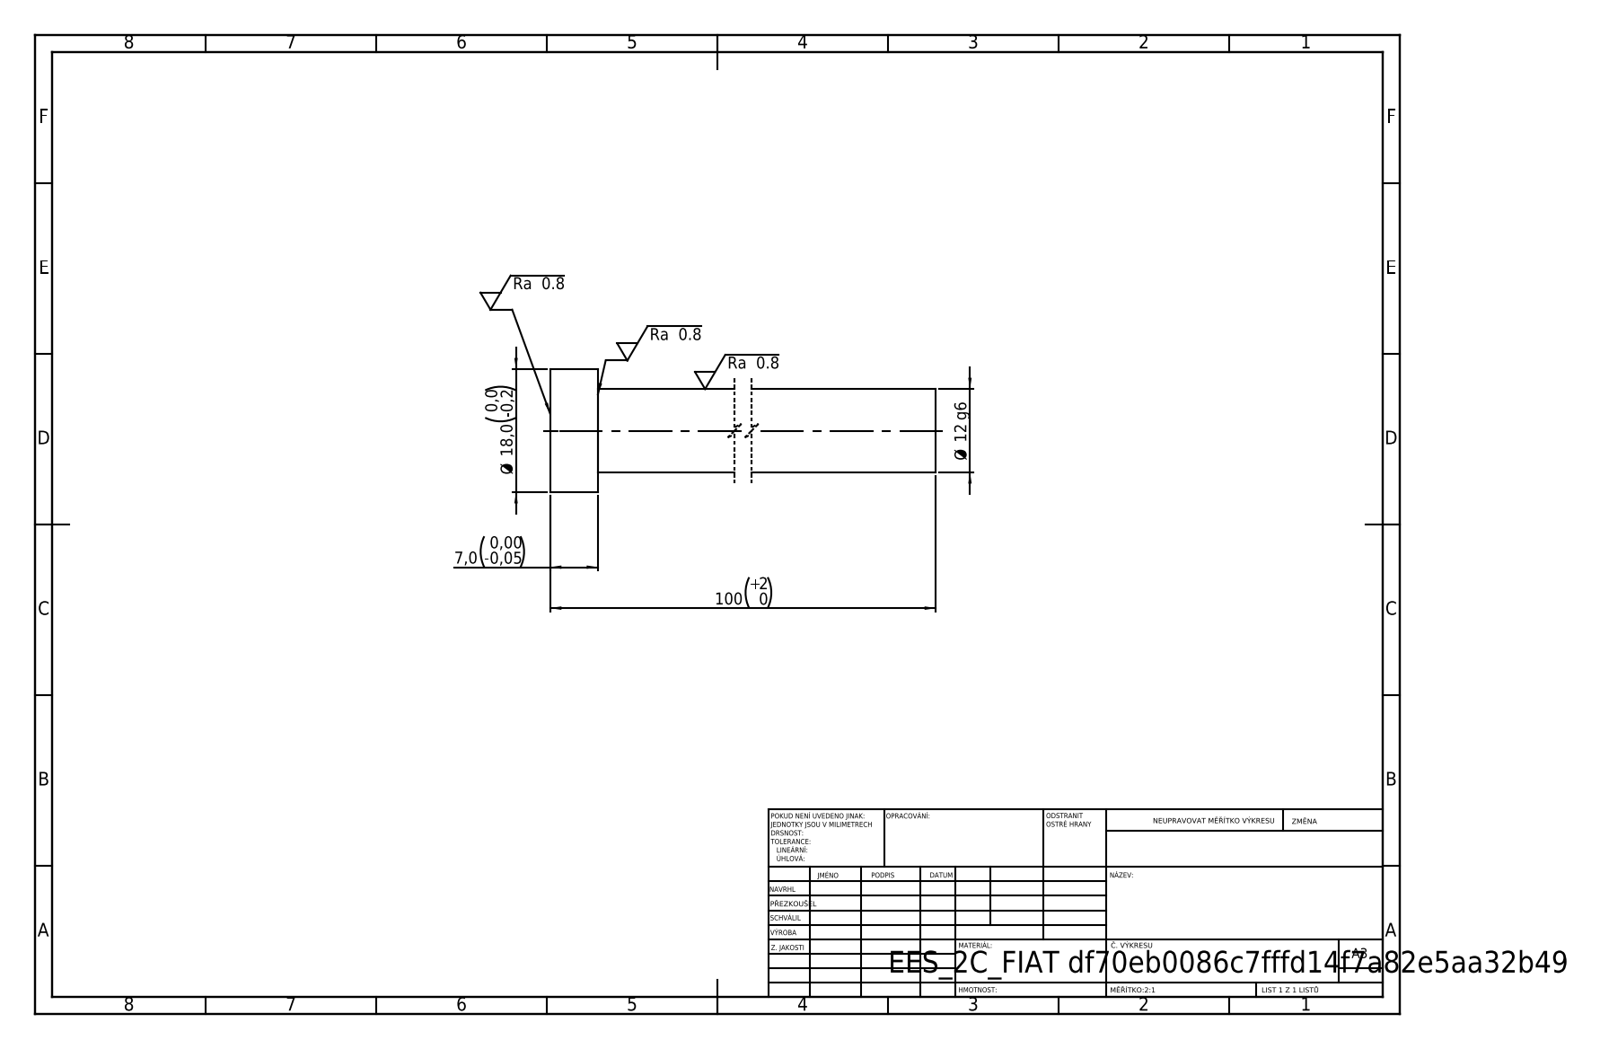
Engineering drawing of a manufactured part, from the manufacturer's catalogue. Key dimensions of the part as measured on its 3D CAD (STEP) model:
STEP written by: SolidWorks 2019 (CONFIG_CONTROL_DESIGN)
Units: millimetres
Bodies: 1 solid, 7 faces (3 planar, 4 cylindrical, 0 other)
Overall size (bounding box): 100 × 18 × 18
Volume: 12 653 mm³ · Surface area: 4 469 mm²
Round bosses / shafts (diameter × count): ⌀18 ×1, ⌀12.2 ×1
Main face-to-face distances: 7, 100, 93
